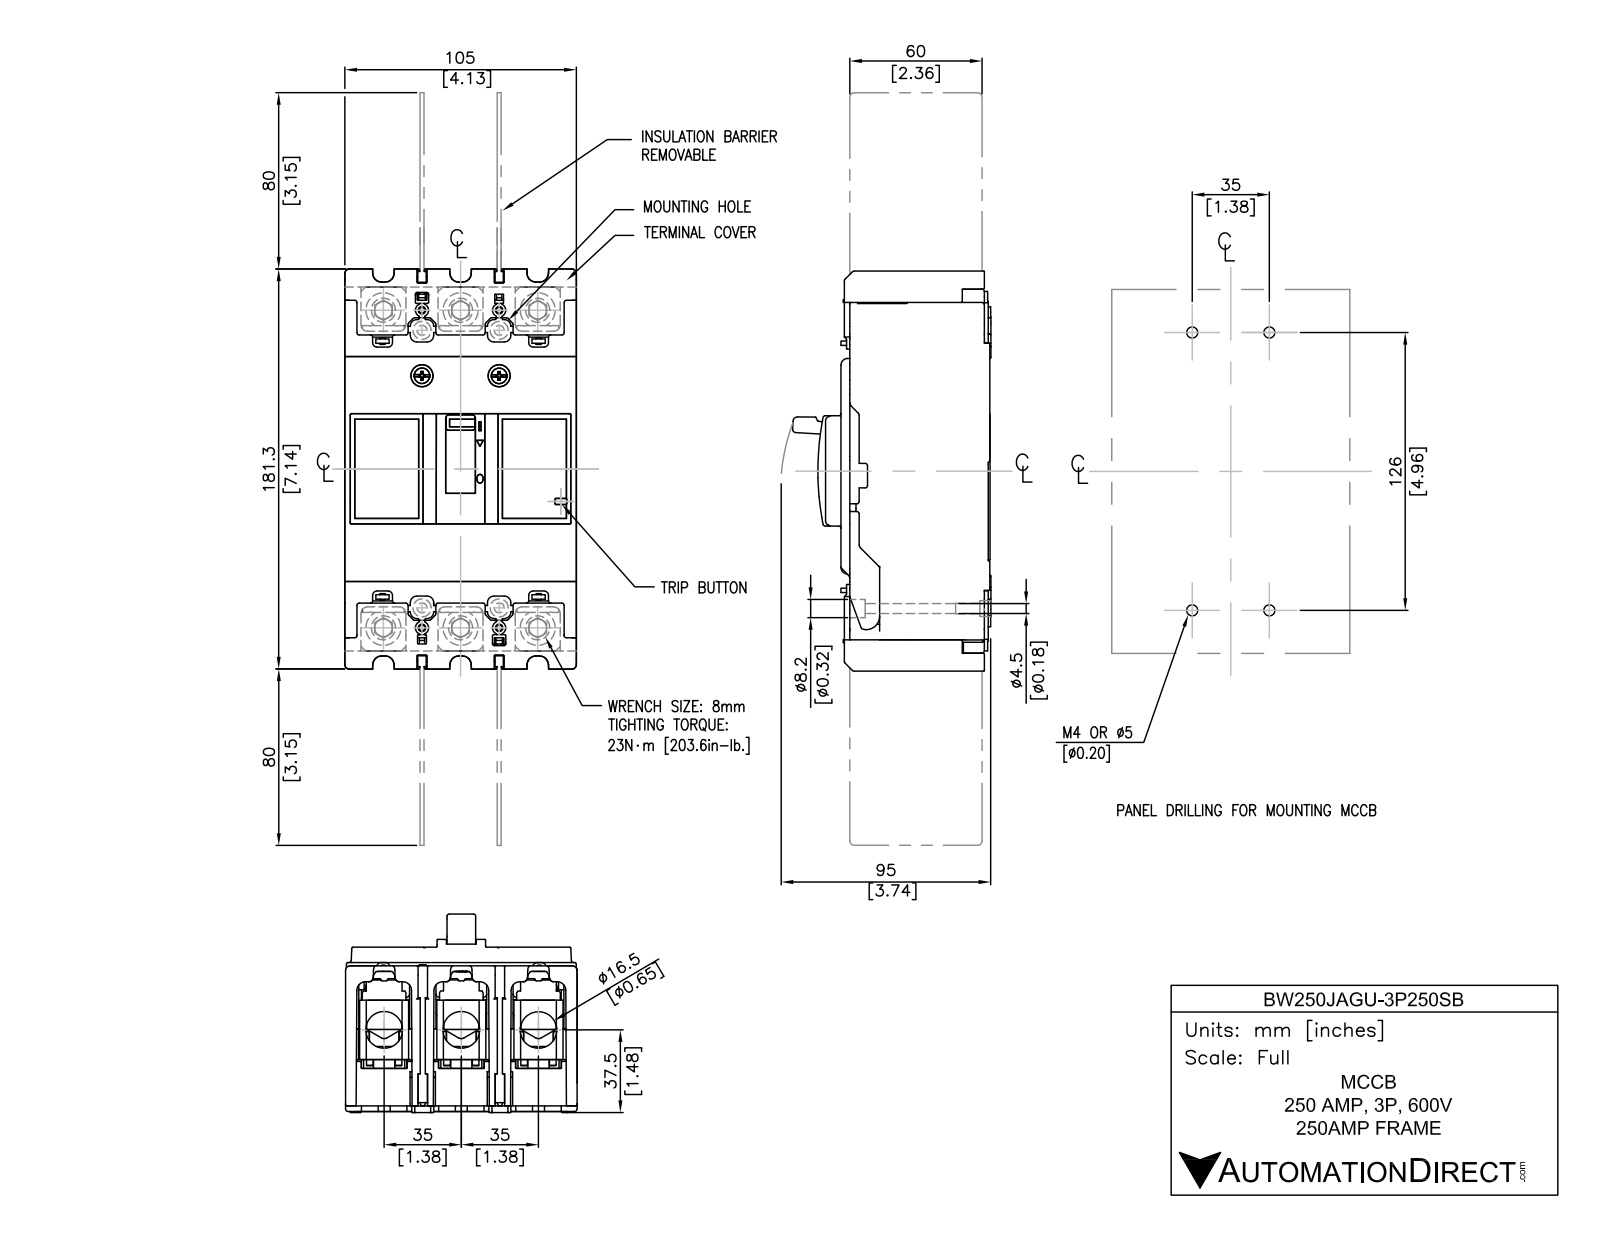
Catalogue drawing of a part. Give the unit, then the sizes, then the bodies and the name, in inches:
Units: inches
Overall size (bounding box): 7.441 × 4.134 × 3.583
Round holes (diameter × count): ⌀0.315 ×6, ⌀0.177 ×4, ⌀0.323 ×4
Round bosses / shafts (diameter × count): ⌀0.512 ×6
Partial cylindrical surfaces — rounded edges, fillets, slot ends (radius × count): R0.039 ×36, R0.118 ×16, R0.079 ×8, R0.492 ×3
Main face-to-face distances: 0.098, 2.5, 4.134, 1.378, 0.787, 2.598, 1.24, 0.335, 0.157, 0.059
Hole centre spacings: 0.775, 5.359, 1.378, 2.097, 5.703, 5.834, 5.669, 2.756
Volume: 67.56 in³ · Surface area: 224 in²
Bodies: 10 solids, 471 faces (338 planar, 121 cylindrical, 12 other)
Part name (STEP PRODUCT): BW250JAGU-3P250SB
STEP written by: SolidWorks 2018 (AUTOMOTIVE_DESIGN)
